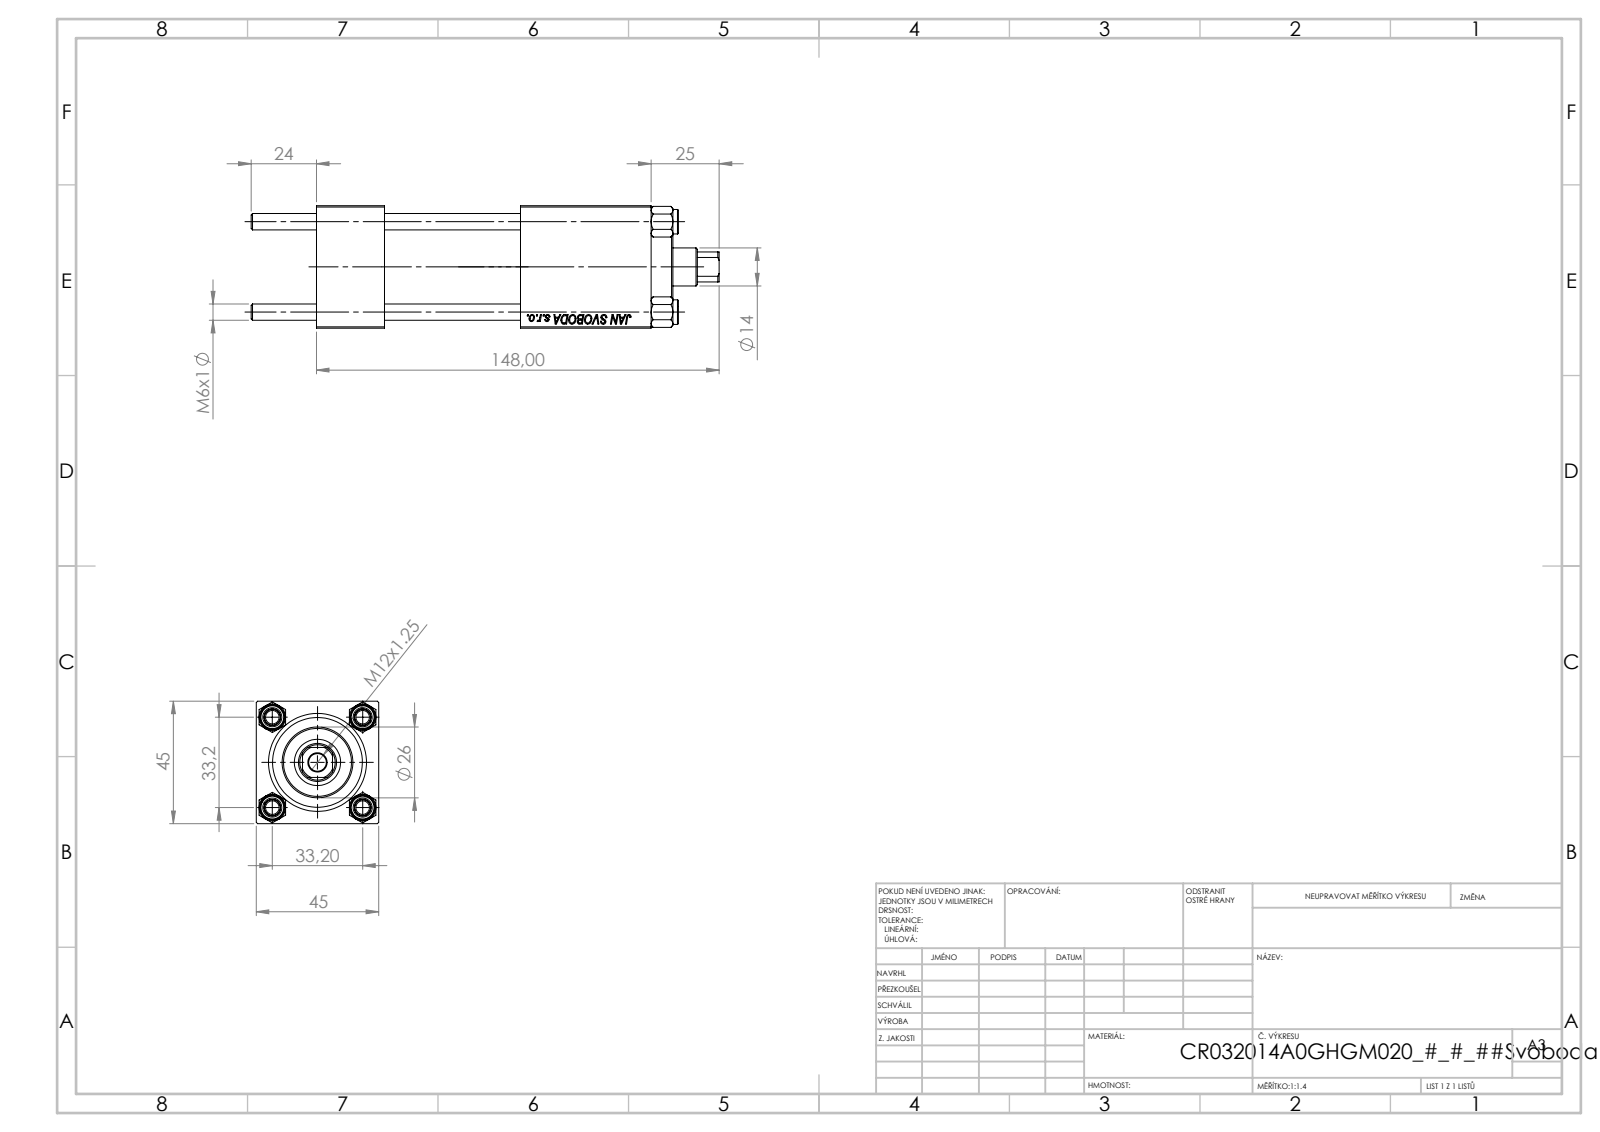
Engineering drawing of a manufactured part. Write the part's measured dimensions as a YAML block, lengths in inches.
part_name: "CR025_012_A_0_G_A_G_M_020_+#_##_TYCINKA; V215CR_BODY_A; NUT_M5; V215CR_VCP (+1 more)"
step_written_by: "SolidWorks 2019 (CONFIG_CONTROL_DESIGN)"
units: inches
bodies: {solids: 11, faces: 1133, planar: 519, cylindrical: 78, other: 536}
overall_size: [6.772, 1.772, 1.772]
volume: 12.1
surface_area: 112.9
round_holes:
  - {diameter: 0.236, count: 4}
  - {diameter: 0.276, count: 2}
  - {diameter: 0.518, count: 2}
  - {diameter: 0.787, count: 2}
  - {diameter: 0.256, count: 1}
  - {diameter: 0.551, count: 1}
  - {diameter: 0.669, count: 1}
  - {diameter: 0.945, count: 1}
  - {diameter: 1.26, count: 1}
  - {diameter: 1.299, count: 1}
round_bosses_or_shafts:
  - {diameter: 0.354, count: 4}
  - {diameter: 1.496, count: 1}
  - {diameter: 1.024, count: 1}
partial_cylinders:
  - {radius: 0.256, count: 1}
face_to_face_distances: [1.772, 0.984, 4.843, 3.858, 1.969, 2.953, 1.89, 3.713, 2.728, 0.76]
hole_center_spacings: [0.924, 1.307, 1.848, 2.972]
